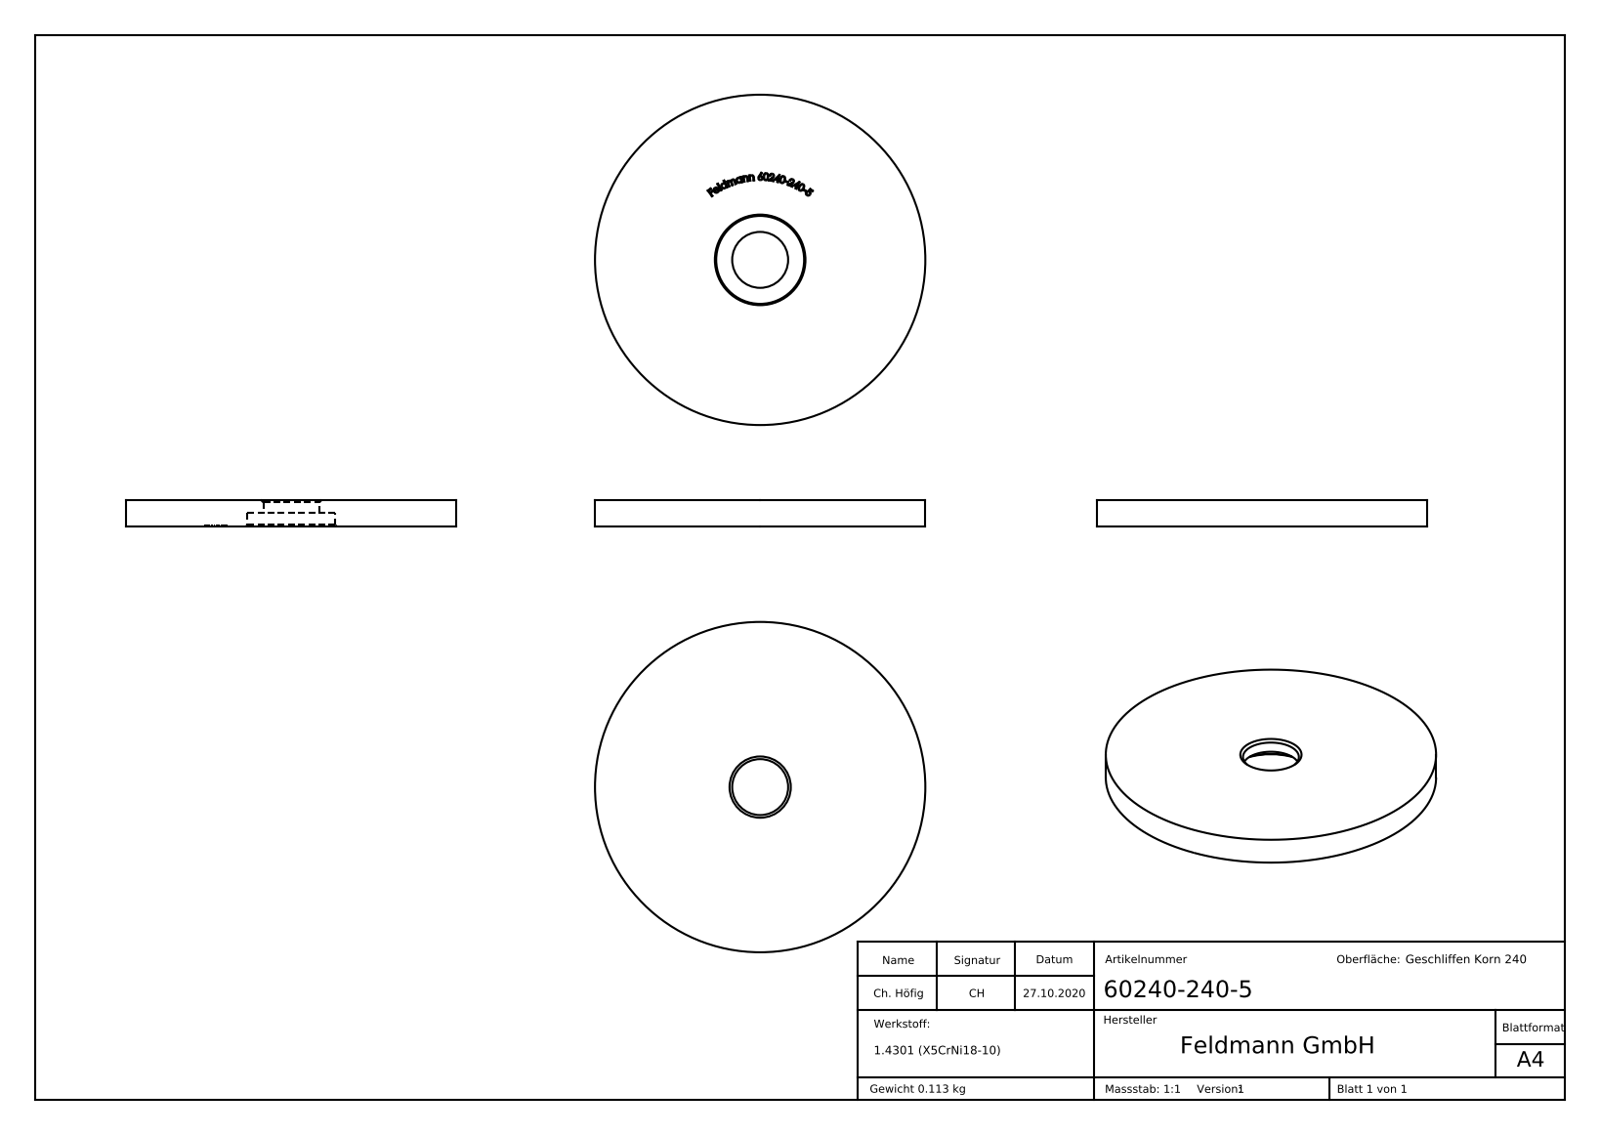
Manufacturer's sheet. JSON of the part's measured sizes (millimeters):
{"part_name": "60240-240-5", "step_written_by": "SolidWorks 2018 (CONFIG_CONTROL_DESIGN)", "units": "millimeters", "bodies": {"solids": 1, "faces": 254, "planar": 140, "cylindrical": 6, "other": 108}, "overall_size": [62, 62, 5], "volume_mm3": 14338, "surface_area_mm2": 7045, "round_holes": [[10.5, 1], [16.5, 1]], "round_bosses_or_shafts": [[62, 1]], "face_to_face_distances": [5, 2.5, 2.4, 4.9, 0.72, 0.54, 0.67, 0.66, 0.79, 1.45]}
